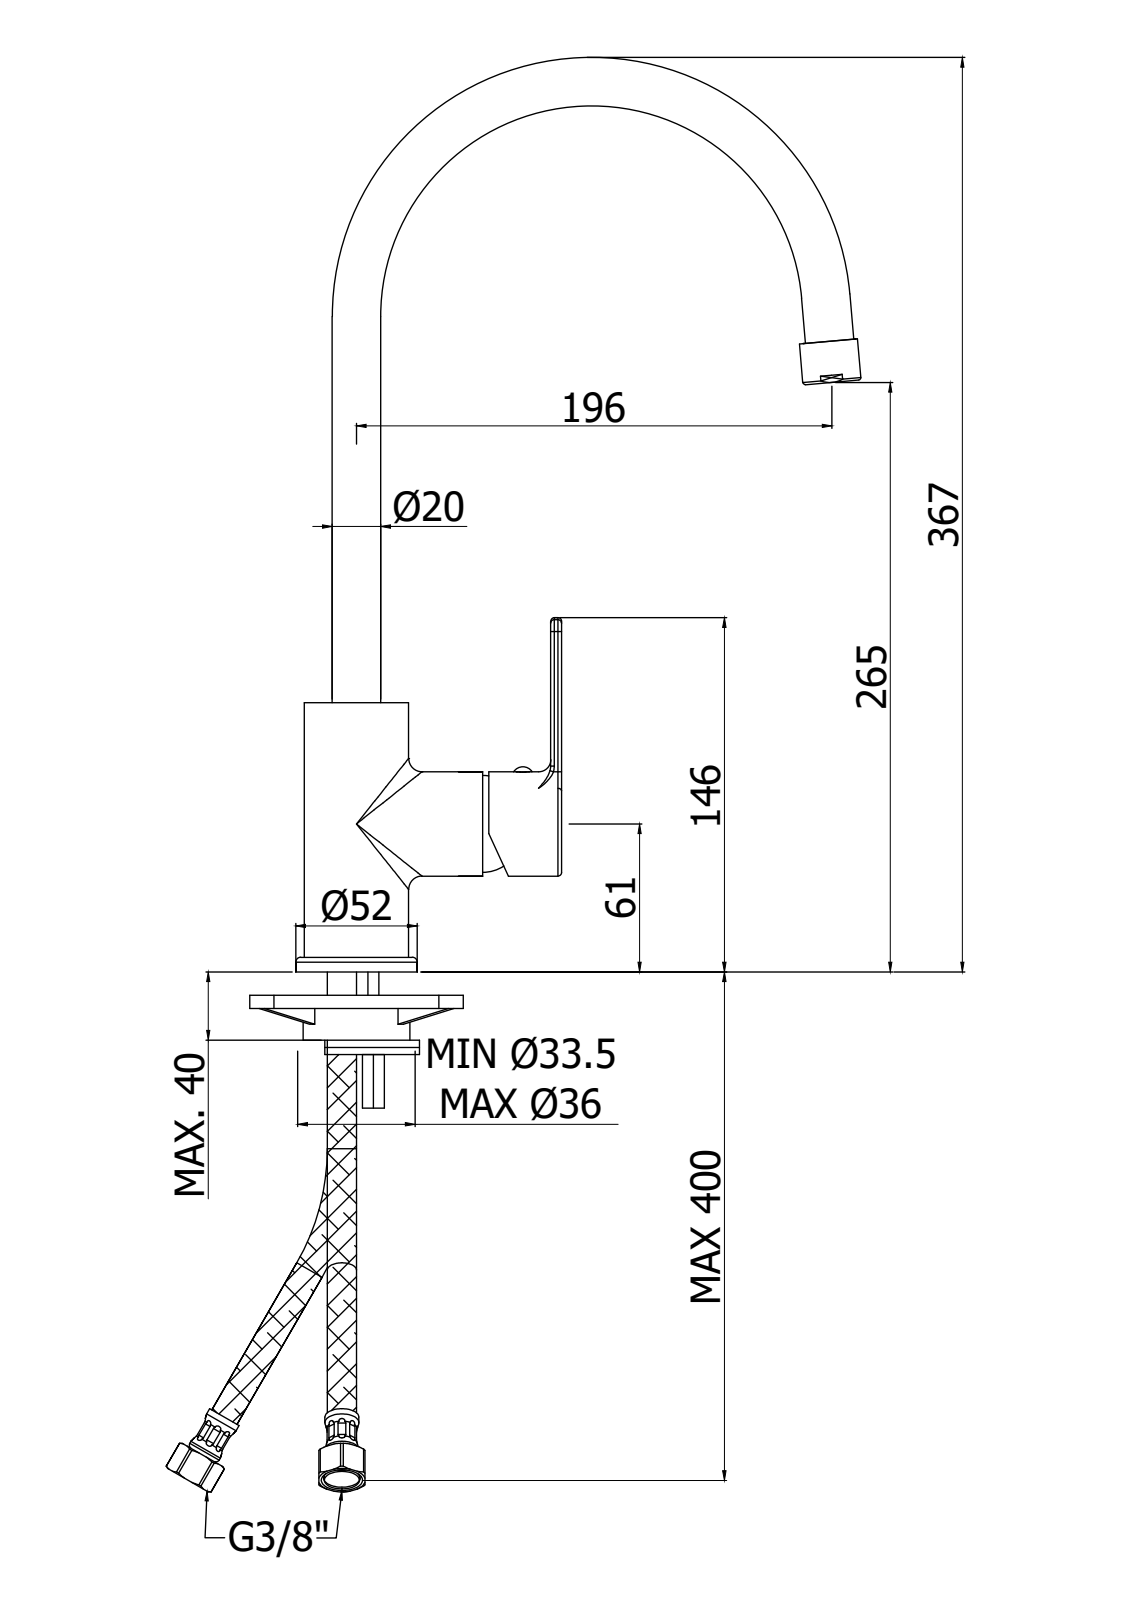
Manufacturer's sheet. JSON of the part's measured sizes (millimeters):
{"part_name": "RED181CR", "step_written_by": "CREO PARAMETRIC BY PTC INC, 2020044 (CONFIG_CONTROL_DESIGN)", "units": "millimeters", "bodies": {"solids": 3, "faces": 3554, "planar": 2525, "cylindrical": 598, "other": 431}, "overall_size": [361.5, 217.51, 111.23], "volume_mm3": 201823, "surface_area_mm2": 134895, "round_holes": [[3, 2], [4, 2], [5.5, 2], [8, 2], [9, 2], [11, 2], [16, 2], [17, 2], [3.3, 1], [3.4, 1], [3.5, 1], [4.5, 1]], "round_bosses_or_shafts": [[44, 2], [19.5, 2], [7.6, 2], [5.5, 2], [52, 1], [43, 1], [42.6, 1], [37.8, 1]], "partial_cylinders_radius": [[0.5, 103], [0.3, 44], [0.2, 16], [24.3, 12], [1.5, 9], [1, 8], [1.7, 6], [5, 4]], "face_to_face_distances": [4.5, 1, 43.3, 3, 3.2, 3.5, 29, 104.5, 2.5, 2], "hole_center_spacings": [8.6, 9.6, 13.04, 13.46, 22.61, 62.97, 75.37, 14]}
